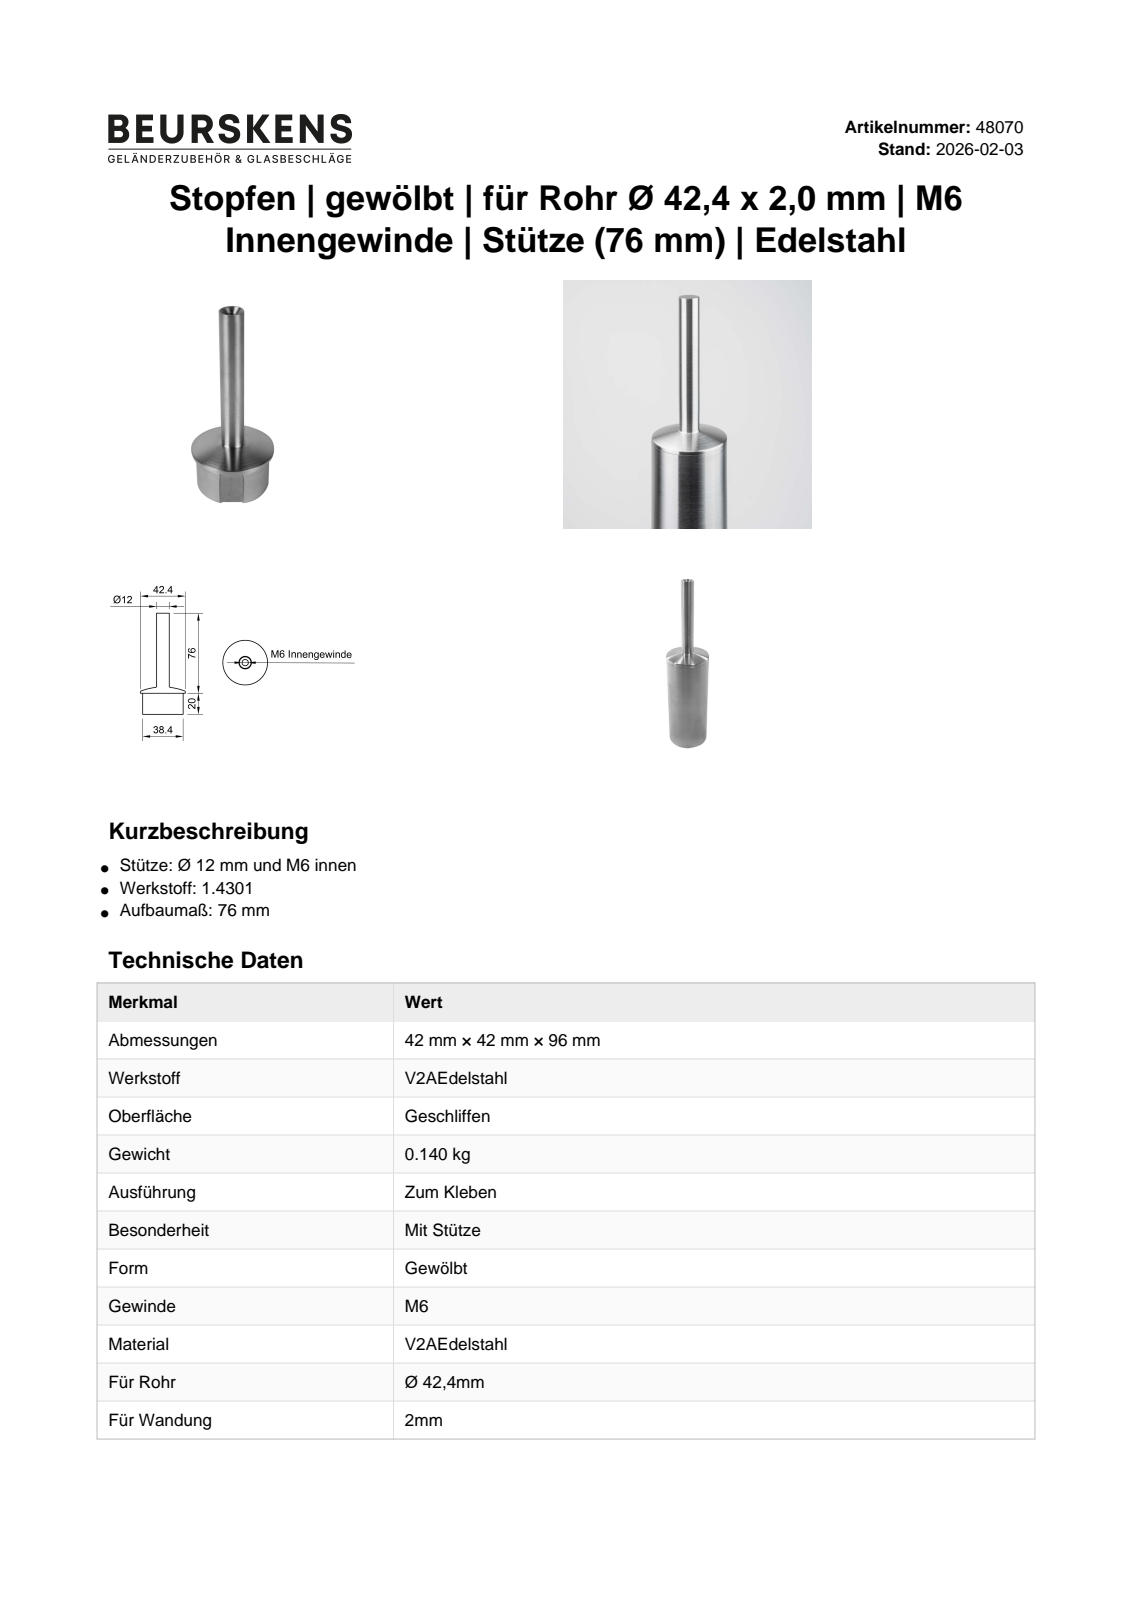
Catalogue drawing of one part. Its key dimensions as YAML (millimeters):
part_name: "48070"
step_written_by: "Autodesk Inventor 2022 (AUTOMOTIVE_DESIGN)"
units: millimeters
bodies: {solids: 1, faces: 19, planar: 6, cylindrical: 6, other: 7}
overall_size: [96, 42.4, 42.4]
volume: 14588
surface_area: 10891
round_holes:
  - {diameter: 6, count: 1}
  - {diameter: 34.4, count: 1}
round_bosses_or_shafts:
  - {diameter: 42.4, count: 1}
  - {diameter: 38.4, count: 1}
  - {diameter: 12, count: 1}
face_to_face_distances: [20, 23.5, 3.5, 96, 76, 72.5, 15, 5, 8.5, 81]
